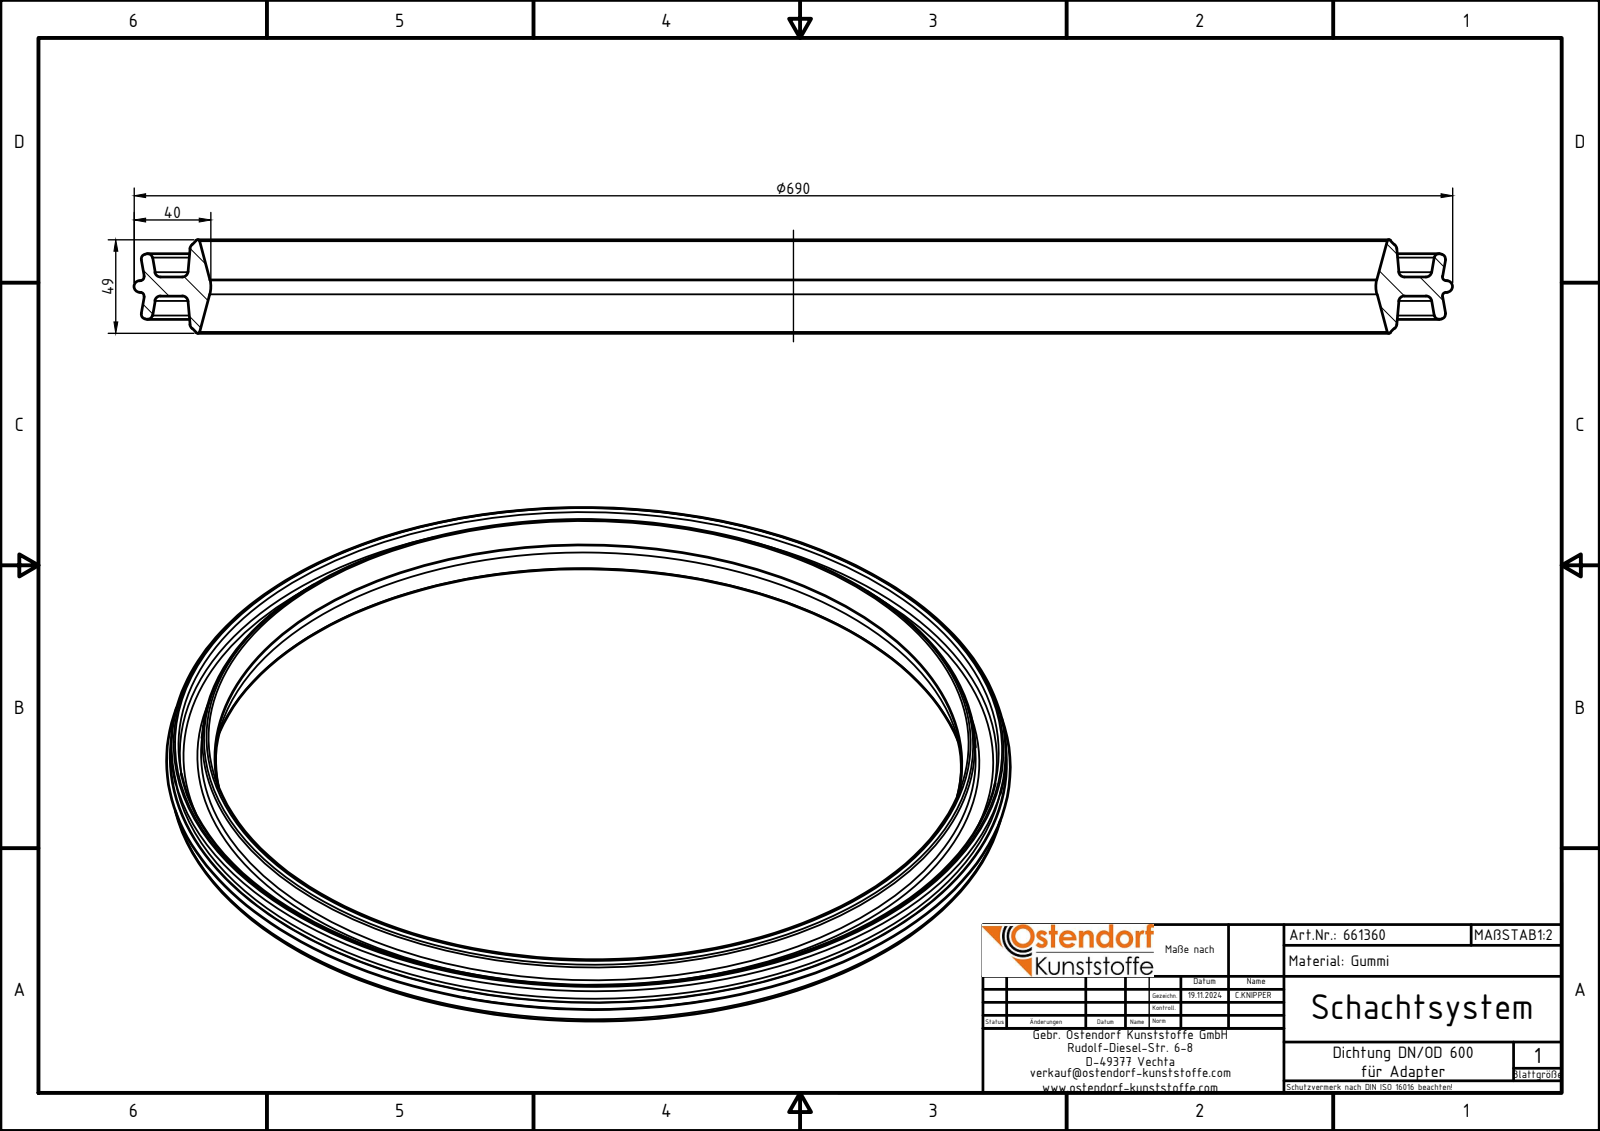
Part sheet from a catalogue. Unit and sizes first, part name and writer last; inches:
Units: inches
Overall size (bounding box): 27.165 × 27.165 × 1.928
Main face-to-face distances: 0.395
Volume: 101 in³ · Surface area: 618.7 in²
Bodies: 1 solid, 32 faces (2 planar, 0 cylindrical, 30 other)
Part name (STEP PRODUCT): 661360z
STEP written by: Autodesk Inventor 2024 (AUTOMOTIVE_DESIGN)
